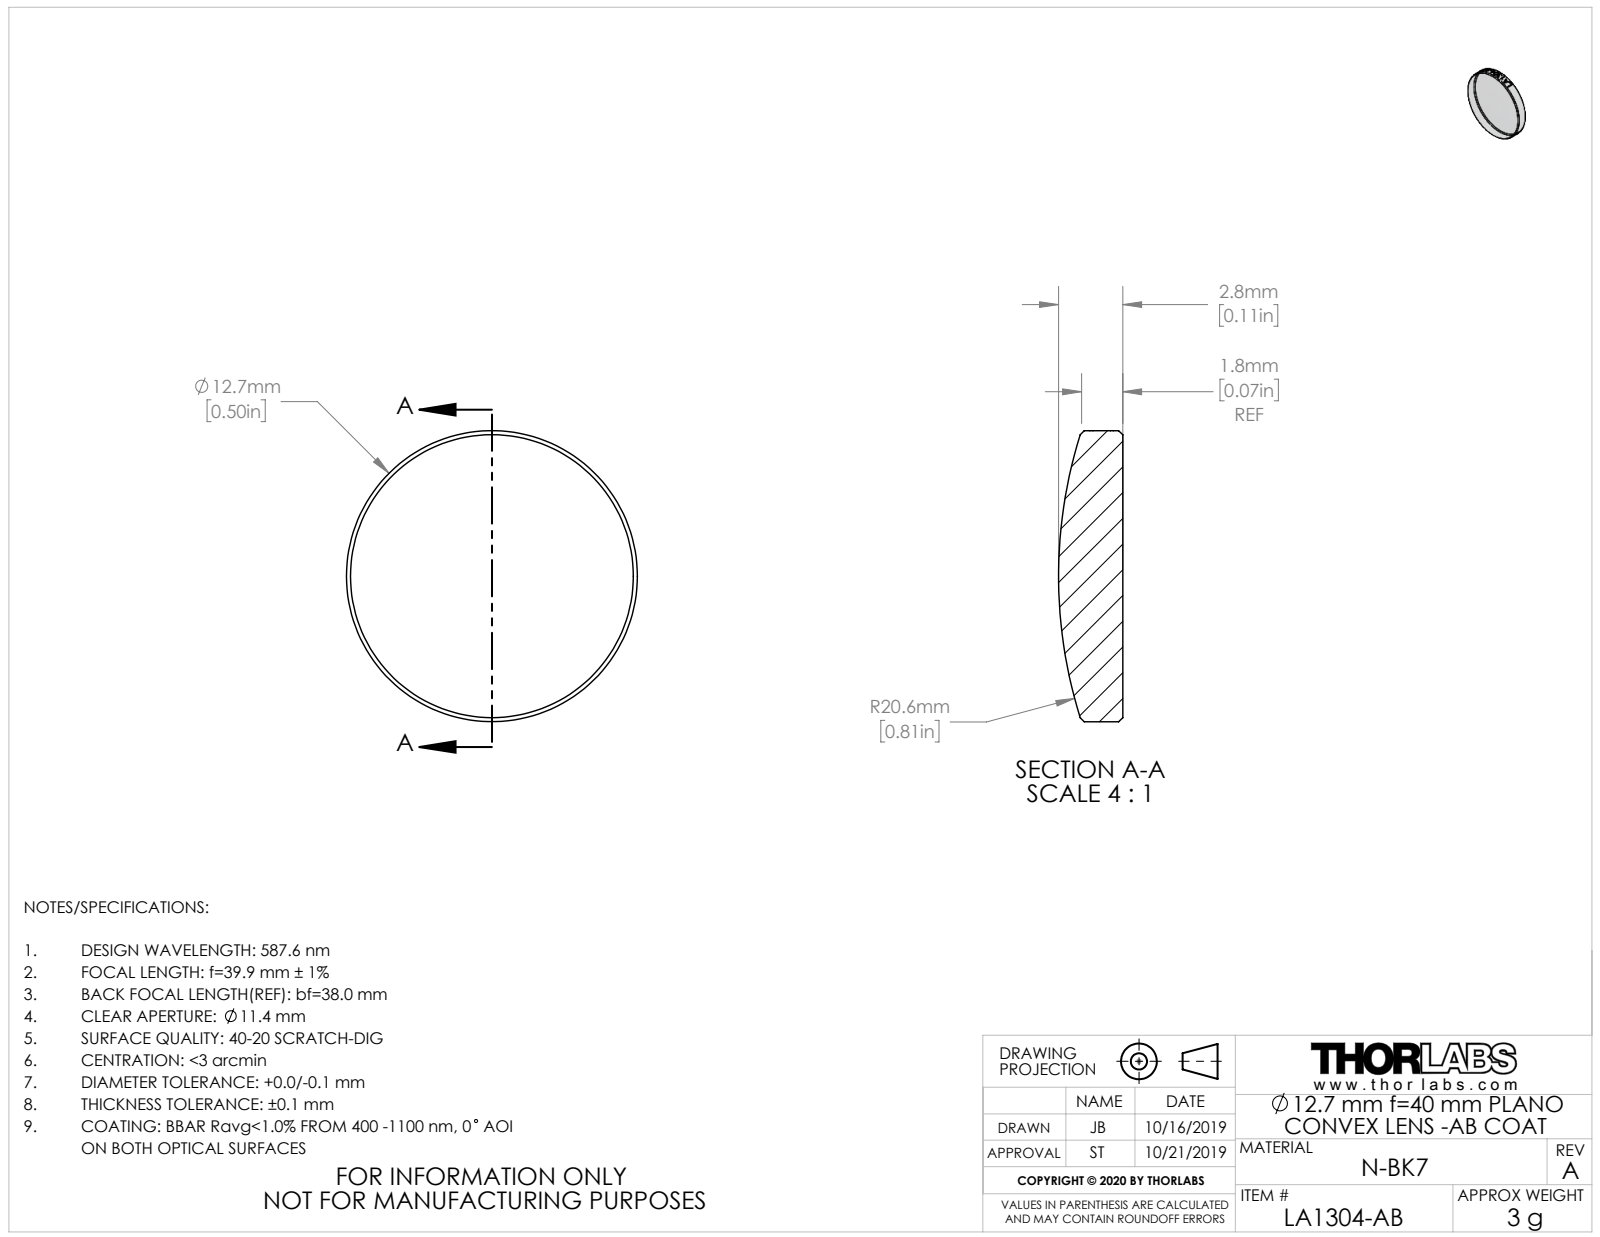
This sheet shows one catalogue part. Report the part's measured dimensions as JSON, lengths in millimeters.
{"part_name": "TTN195793-E0W", "step_written_by": "SolidWorks 2018 (CONFIG_CONTROL_DESIGN)", "units": "millimeters", "bodies": {"solids": 1, "faces": 28, "planar": 1, "cylindrical": 21, "other": 6}, "overall_size": [12.7, 12.7, 2.8], "volume_mm3": 291, "surface_area_mm2": 322, "round_bosses_or_shafts": [[12.7, 1]]}
